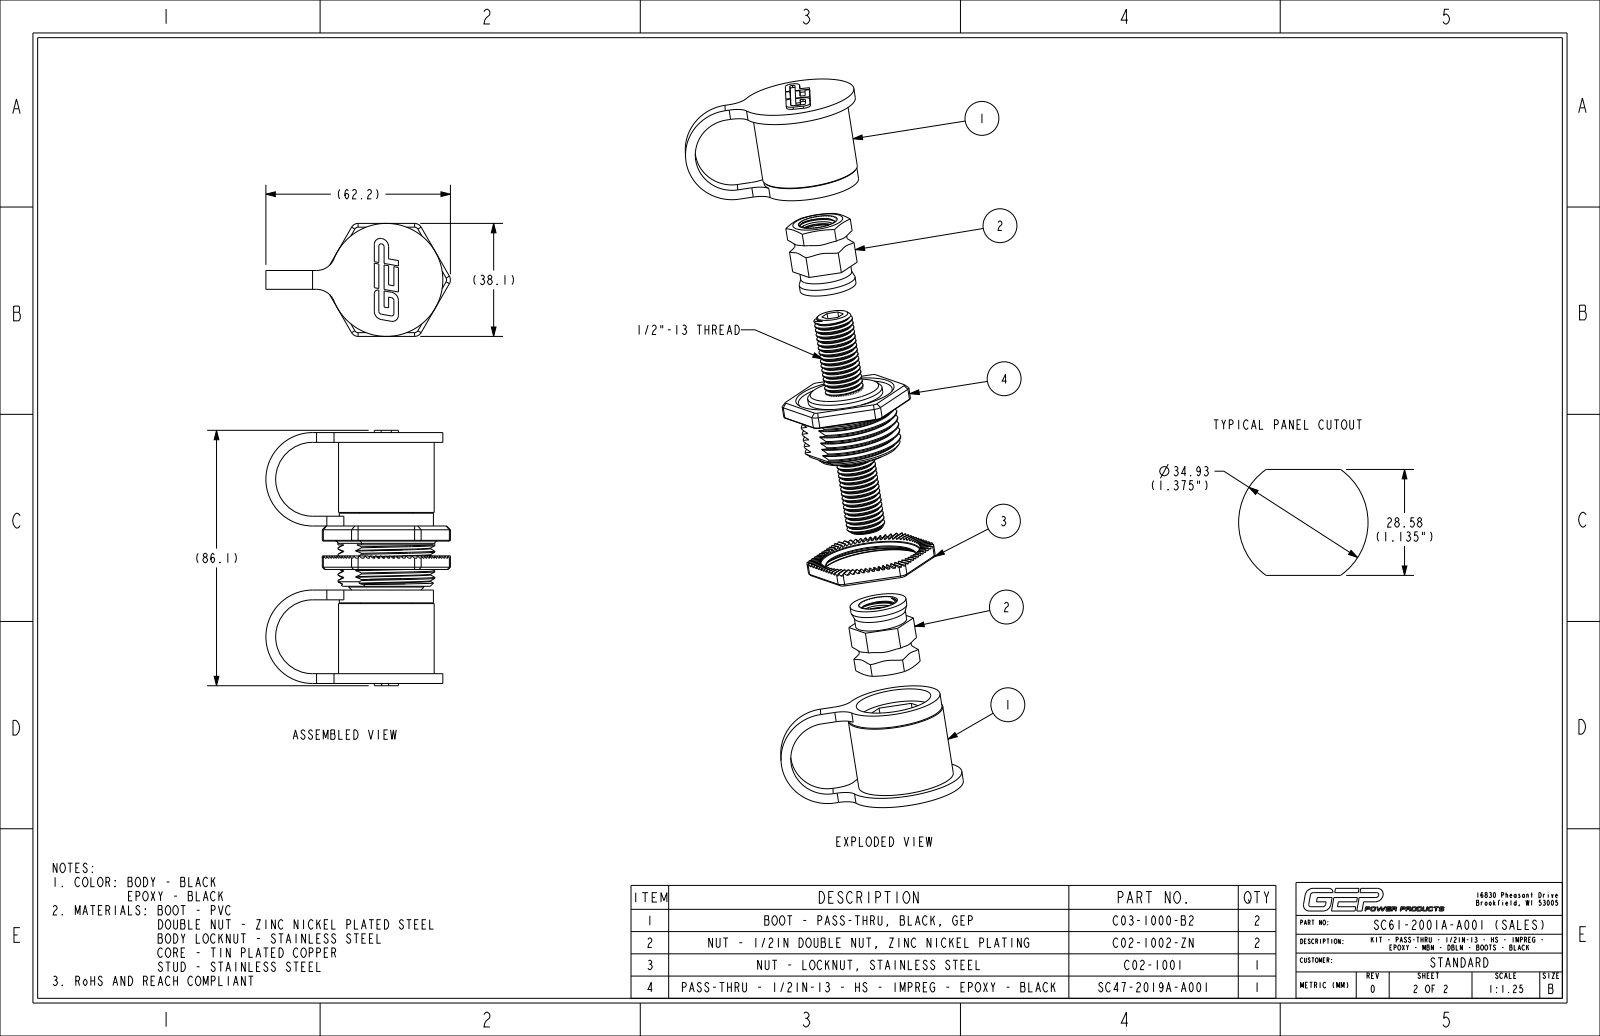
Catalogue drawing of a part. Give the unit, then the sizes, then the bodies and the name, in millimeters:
Units: millimetres
Overall size (bounding box): 86.1 × 55.8 × 44.7
Round holes (diameter × count): ⌀10.7 ×1, ⌀21.3 ×1, ⌀25.4 ×1, ⌀32 ×1, ⌀34.2 ×1
Round bosses / shafts (diameter × count): ⌀38.1 ×1, ⌀32.3 ×1, ⌀32 ×1, ⌀31.8 ×1, ⌀19.1 ×1, ⌀17.4 ×1, ⌀13 ×1
Partial cylindrical surfaces — rounded edges, fillets, slot ends (radius × count): R0.8 ×6, R1 ×6, R2.5 ×6, R2.8 ×6, R4.6 ×6, R2 ×4, R6.4 ×4, R1.3 ×2
Main face-to-face distances: 19.1, 31.5, 53.1, 3.3, 81.3, 6.4, 28.2, 49.8, 84.6, 4.3
Volume: 70 810 mm³ · Surface area: 43 990 mm²
Bodies: 10 solids, 1290 faces (742 planar, 289 cylindrical, 259 other)
Part name (STEP PRODUCT): C07-1002_NCF; PC40-2005A-B001_MOLD_NCF; PC40-2005A-B001_NCF_ASM; PC05-2016A-A000_NCF (+8 more)
STEP written by: CREO PARAMETRIC BY PTC INC, 2024014 (CONFIG_CONTROL_DESIGN)
